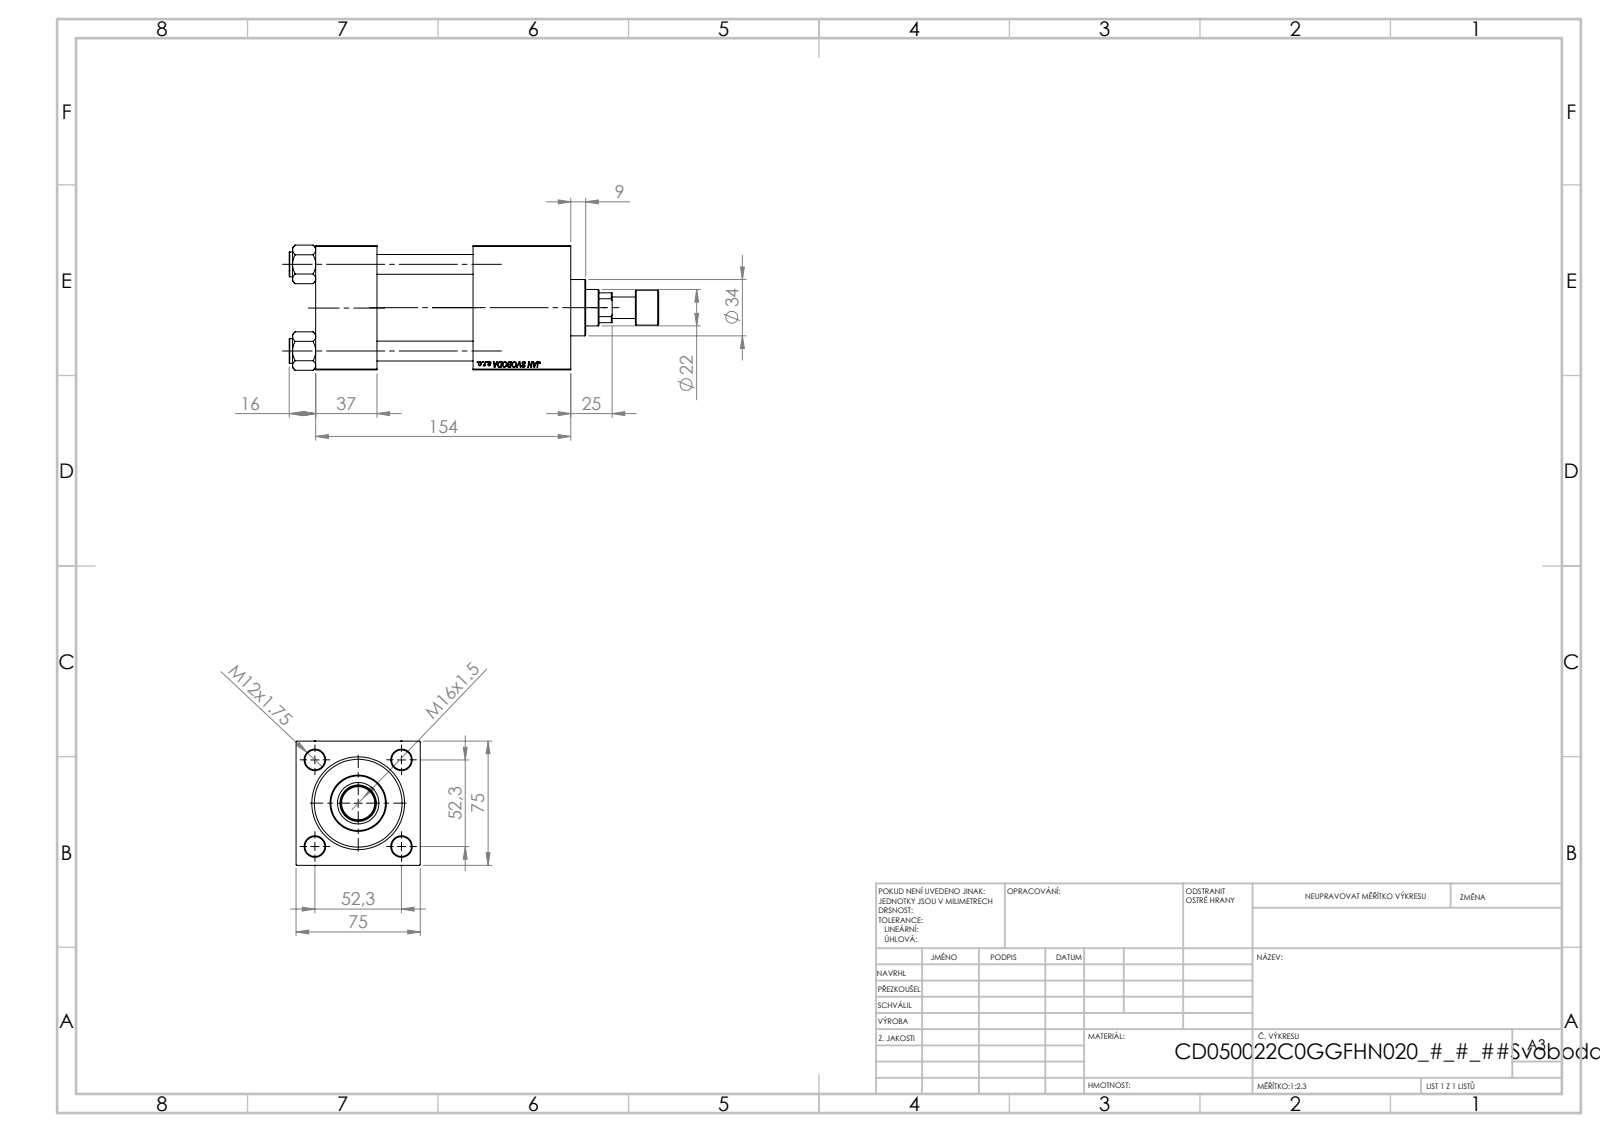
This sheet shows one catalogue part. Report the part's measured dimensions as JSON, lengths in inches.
{"part_name": "V215CR_ROD_END_F; V215CD_VC_C; NUT_M5_V215CD_C; V215CD_Body_C (+2 more)", "step_written_by": "SolidWorks 2019 (CONFIG_CONTROL_DESIGN)", "units": "inches", "bodies": {"solids": 12, "faces": 1160, "planar": 529, "cylindrical": 91, "other": 540}, "overall_size": [8.78, 2.974, 2.953], "volume_in3": 40.49, "surface_area_in2": 231.6, "round_holes": [[0.472, 4], [0.276, 2], [0.825, 2], [1.181, 2], [0.413, 1], [0.866, 1], [0.984, 1], [1.614, 1], [1.969, 1], [2.087, 1]], "round_bosses_or_shafts": [[0.591, 4], [2.205, 1], [1.339, 1], [0.827, 1], [0.512, 1]], "face_to_face_distances": [2.953, 1.457, 6.063, 4.606, 2.323, 3.74, 2.283, 4.933, 3.476, 1.193], "hole_center_spacings": [1.456, 2.059, 2.912, 3.681]}
